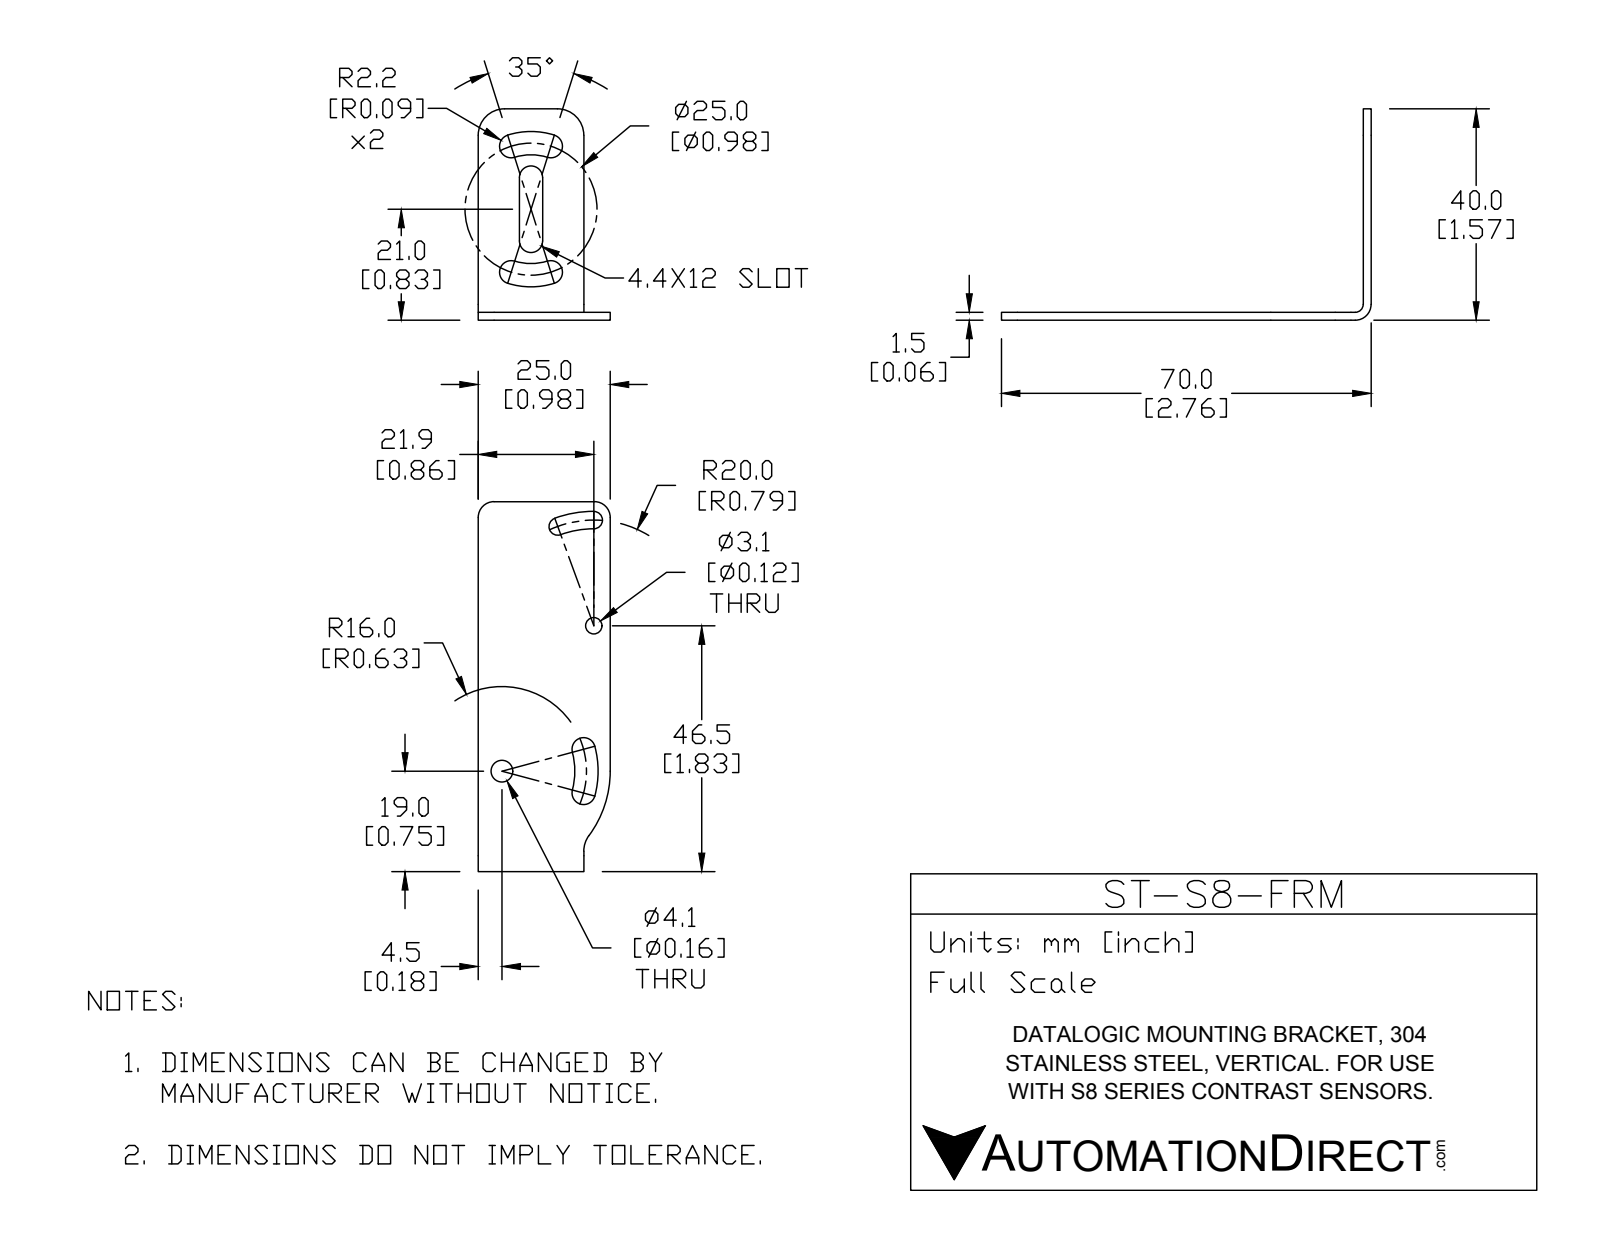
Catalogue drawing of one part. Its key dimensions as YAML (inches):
part_name: "ST-S8-FRM"
step_written_by: "SolidWorks 2016 (AUTOMOTIVE_DESIGN)"
units: inches
bodies: {solids: 1, faces: 44, planar: 11, cylindrical: 33, other: 0}
overall_size: [2.756, 1.575, 0.984]
volume: 0.198
surface_area: 7.713
round_holes:
  - {diameter: 0.122, count: 1}
  - {diameter: 0.161, count: 1}
partial_cylinders:
  - {radius: 0.087, count: 8}
  - {radius: 0.118, count: 3}
  - {radius: 0.197, count: 3}
  - {radius: 0.065, count: 2}
  - {radius: 0.059, count: 1}
  - {radius: 0.406, count: 1}
  - {radius: 0.543, count: 1}
  - {radius: 0.579, count: 1}
face_to_face_distances: [0.059, 0.984, 0.787, 0.197, 0.307, 0.48, 2.756, 2.697, 0.173, 0.677]
hole_center_spacings: [1.281]
